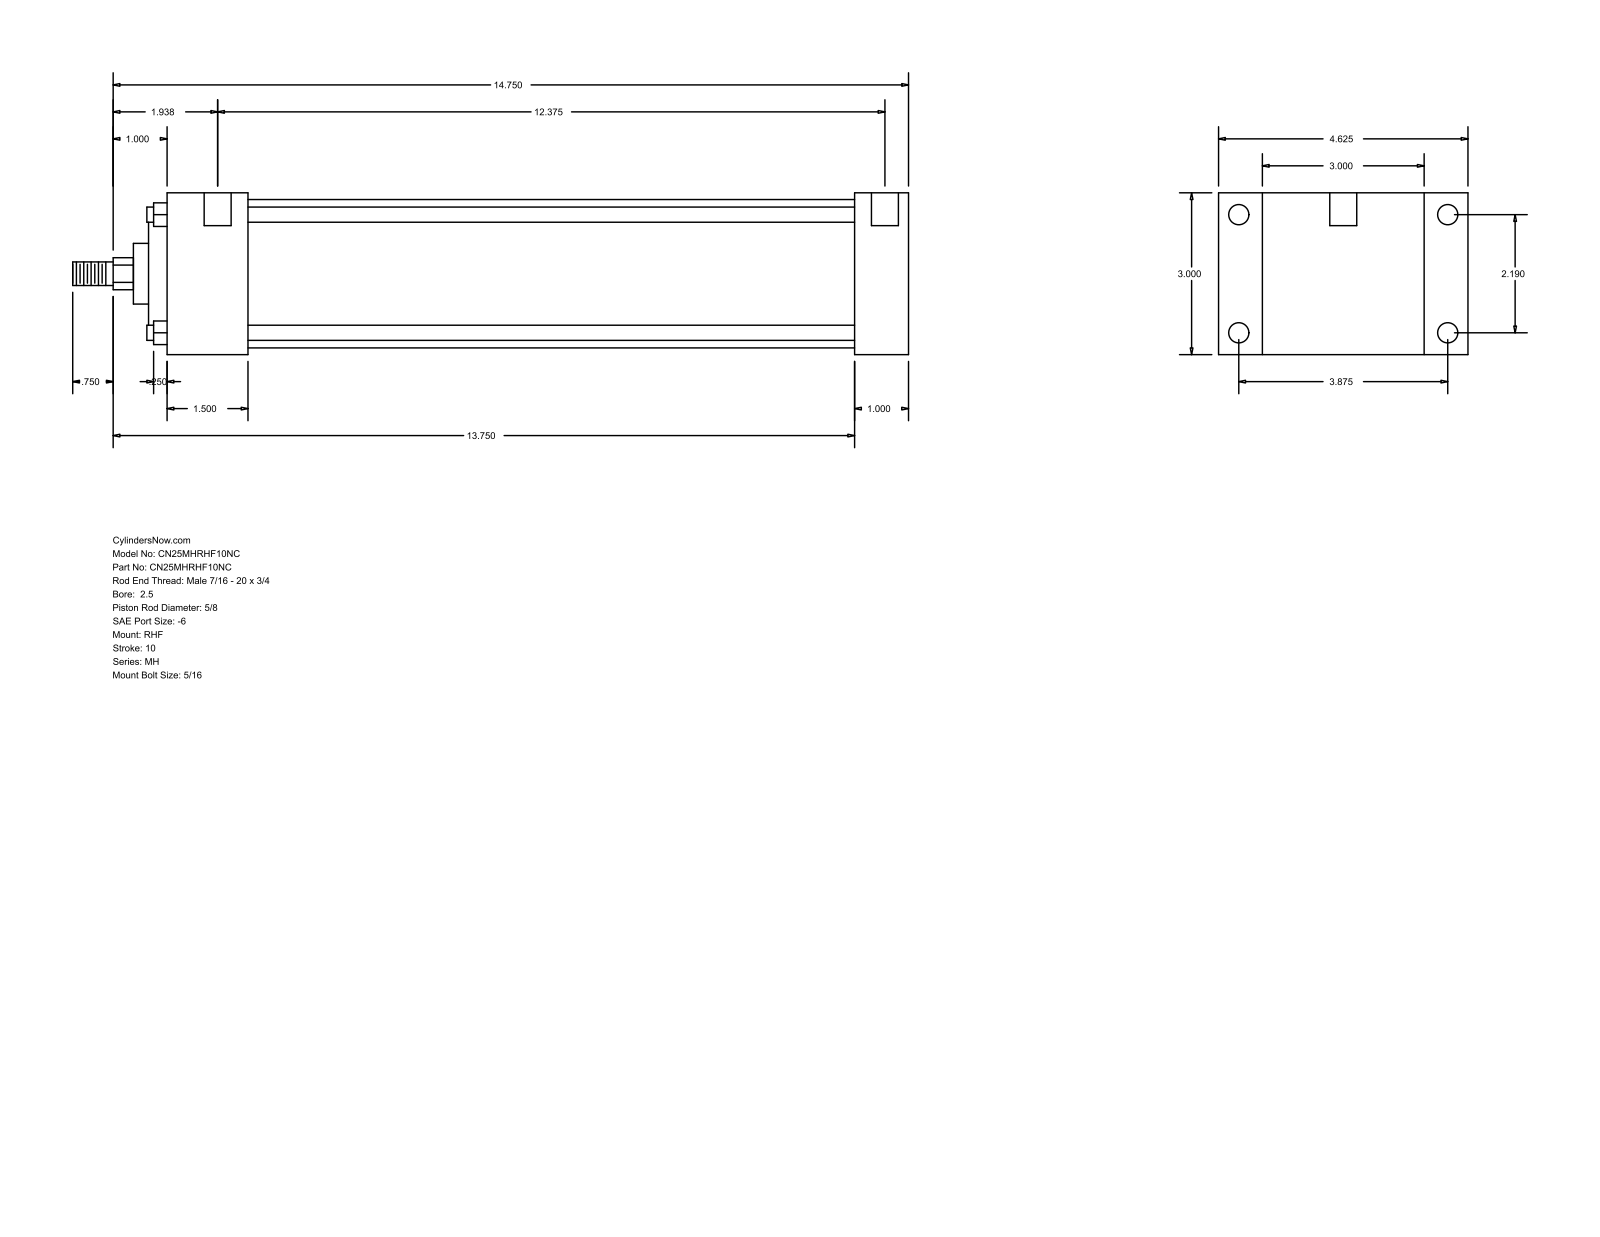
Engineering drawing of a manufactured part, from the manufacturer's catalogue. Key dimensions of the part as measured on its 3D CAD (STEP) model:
Part name (STEP PRODUCT): MH_RHF__0250_0.625
STEP written by: GSSL Pune (CONFIG_CONTROL_DESIGN)
Units: millimetres
Bodies: 0 solids, 90 faces (61 planar, 29 cylindrical, 0 other)
Overall size (bounding box): 393.7 × 117.47 × 76.2
Round holes (diameter × count): ⌀5.56 ×4, ⌀9.53 ×4, ⌀12.7 ×2
Round bosses / shafts (diameter × count): ⌀7.14 ×4, ⌀69.85 ×1, ⌀55.55 ×1, ⌀28.57 ×1, ⌀15.88 ×1, ⌀11.11 ×1
Partial cylindrical surfaces — rounded edges, fillets, slot ends (radius × count): R7.54 ×1
Main face-to-face distances: 76.2, 25.4, 20.64, 96.84, 349.25, 323.85, 38.1, 117.48, 285.75, 311.15
Hole centre spacings: 55.62, 98.42, 113.05, 322.26, 3.17, 4.76, 314.33, 317.5
